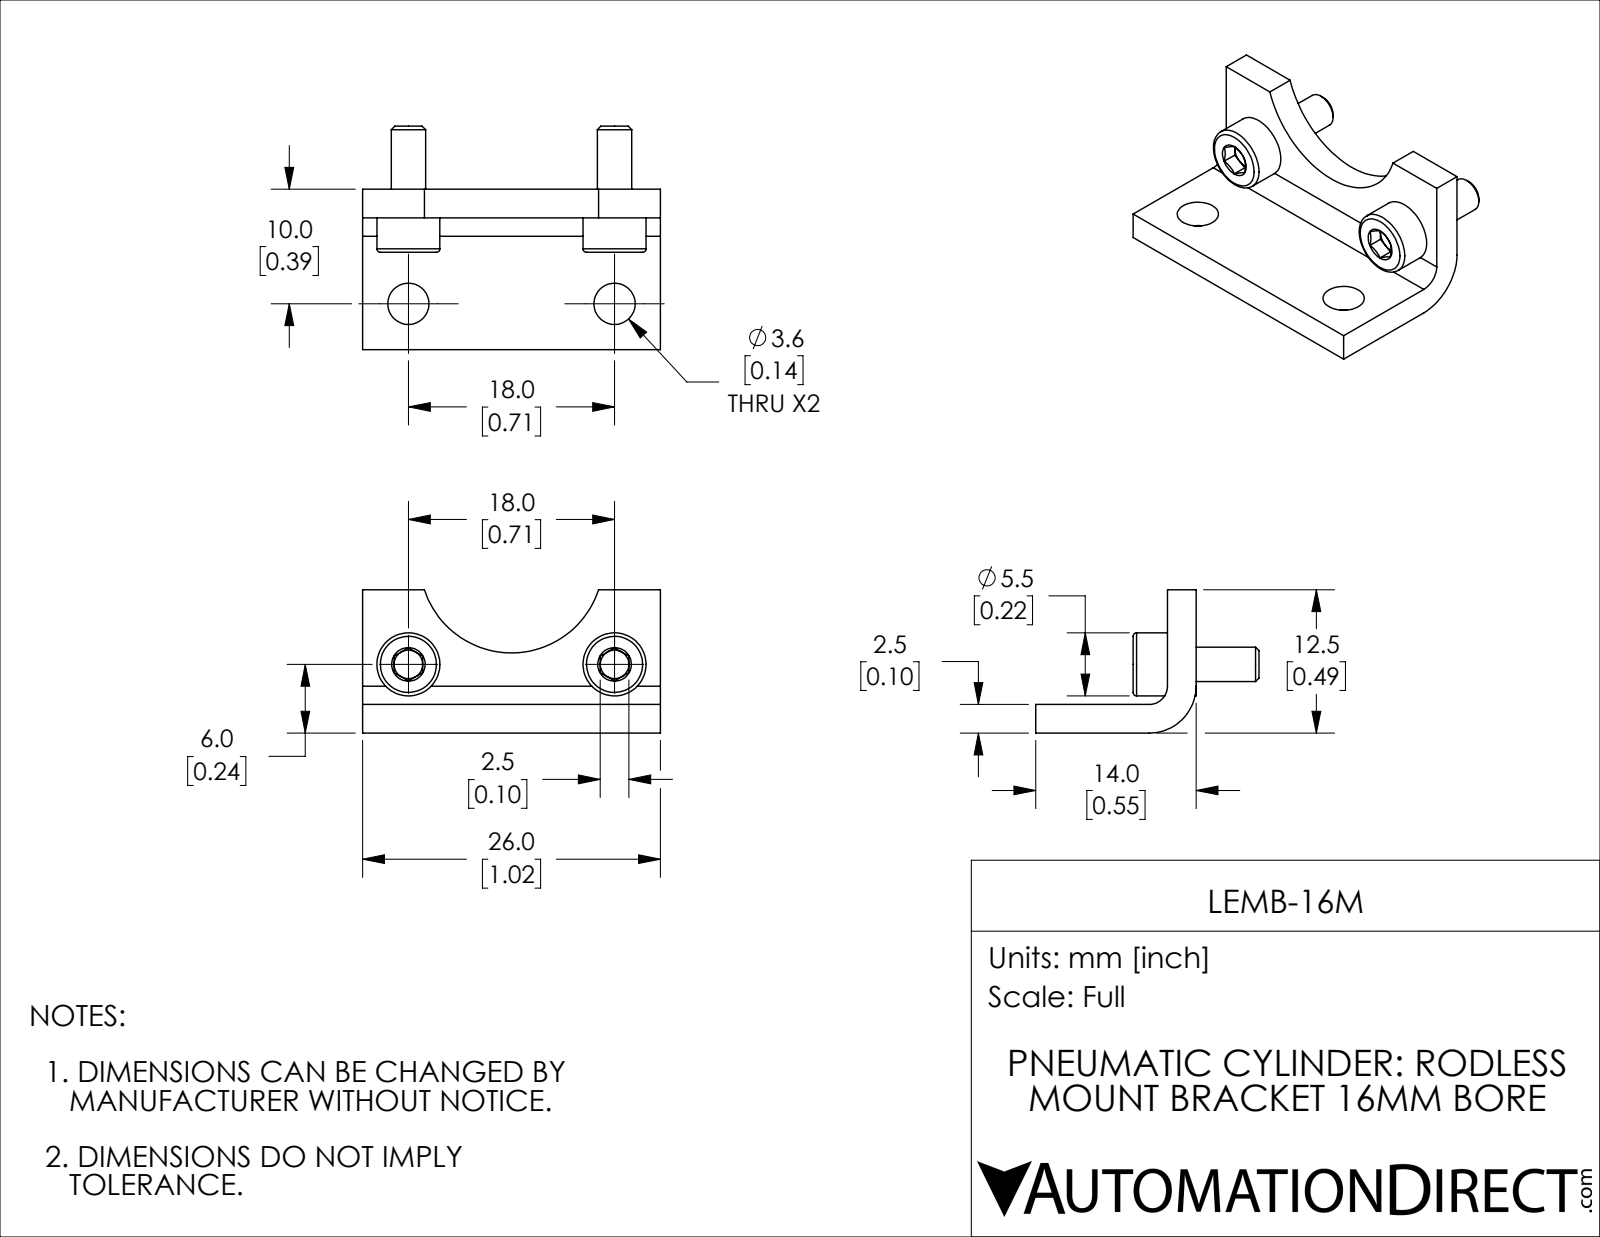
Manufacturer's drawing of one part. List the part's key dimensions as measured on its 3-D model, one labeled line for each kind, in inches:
Part name (STEP PRODUCT): LEMB-16M
STEP written by: SolidWorks 2019 (CONFIG_CONTROL_DESIGN)
Units: inches
Bodies: 3 solids, 88 faces (39 planar, 21 cylindrical, 28 other)
Overall size (bounding box): 1.024 × 0.768 × 0.492
Volume: 0.09 in³ · Surface area: 2.657 in²
Round holes (diameter × count): ⌀0.118 ×2, ⌀0.142 ×2
Round bosses / shafts (diameter × count): ⌀0.217 ×2
Partial cylindrical surfaces — rounded edges, fillets, slot ends (radius × count): R0.063 ×1, R0.161 ×1, R0.315 ×1
Main face-to-face distances: 0.098, 0.453, 0.551, 1.024, 0.217, 0.492, 0.394, 0.118, 0.335, 0.315
Hole centre spacings: 0.709
